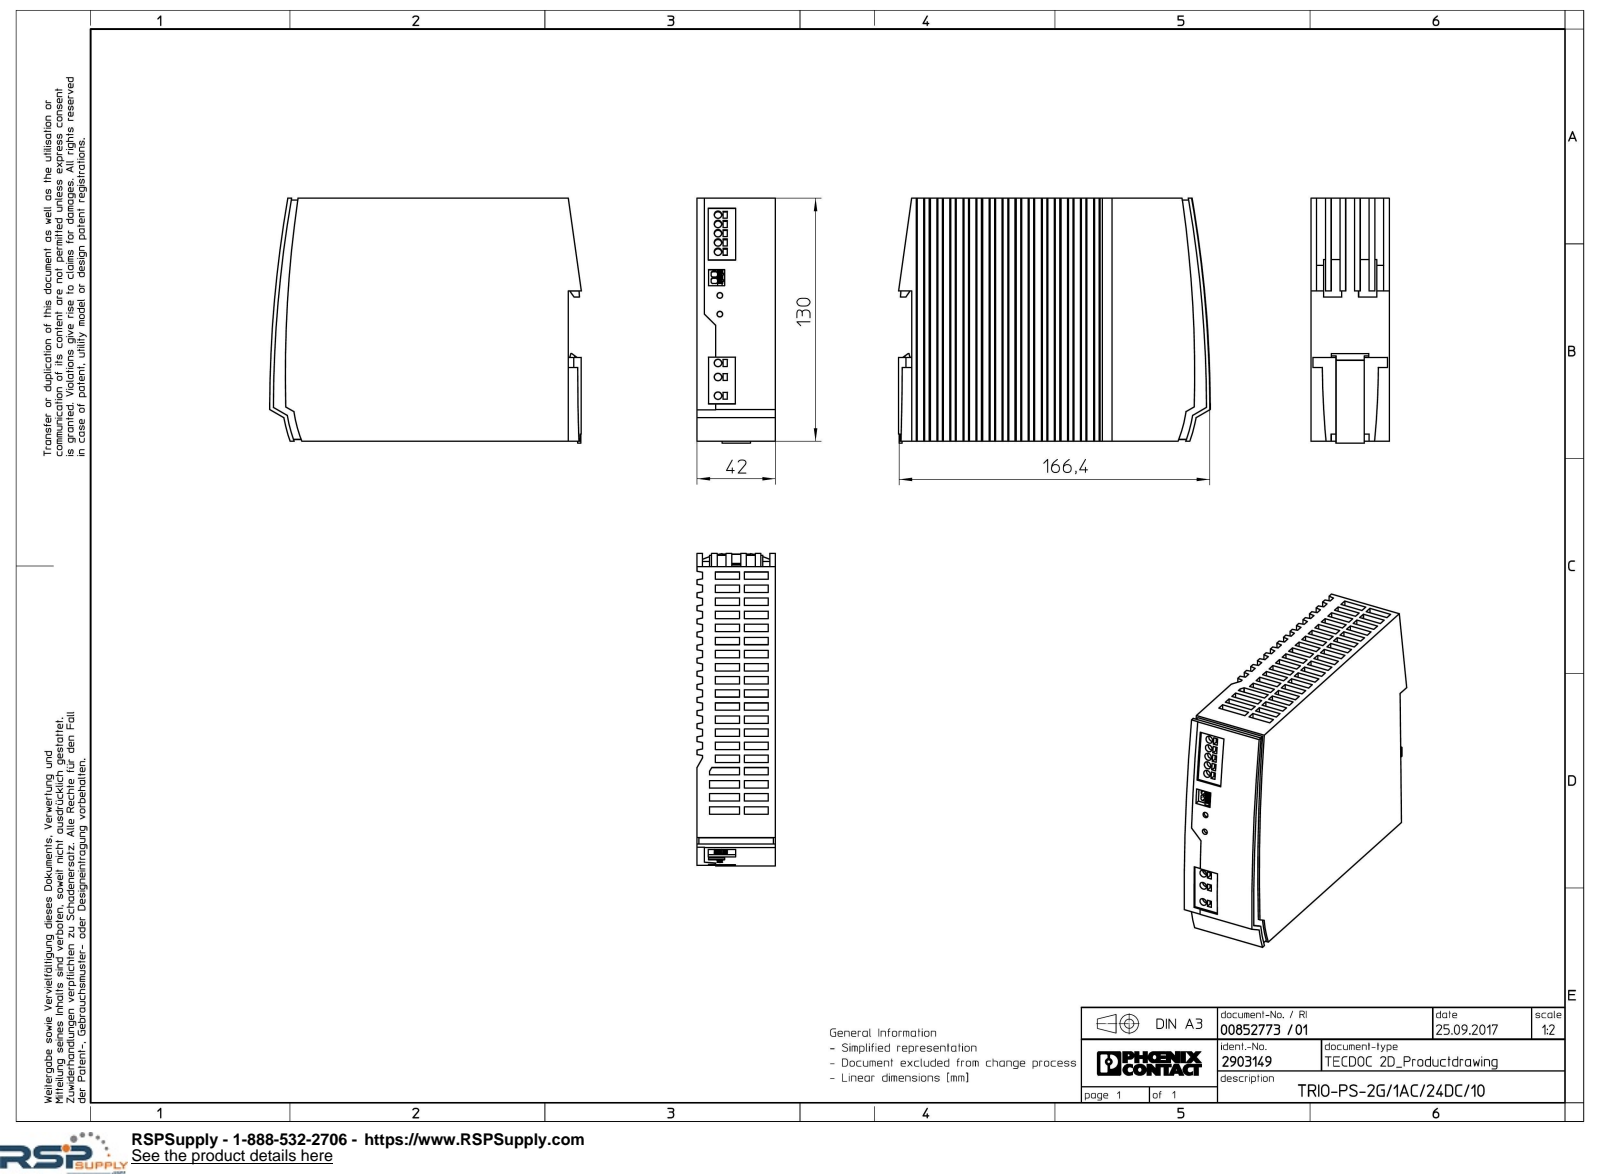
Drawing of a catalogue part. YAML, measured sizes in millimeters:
part_name: "TRIO_PS_2G_1AC_24DC_10-select"
step_written_by: "Creo Elements/Direct Modeling 20.1A 29-Sep-2018 (C) Parametric Technology GmbH (AUTOMOTIVE_DESIGN)"
units: millimeters
bodies: {solids: 1, faces: 694, planar: 647, cylindrical: 43, other: 4}
overall_size: [167, 131, 42]
volume: 826516
surface_area: 86353
round_holes:
  - {diameter: 4, count: 8}
  - {diameter: 3, count: 2}
partial_cylinders:
  - {radius: 0.57, count: 2}
  - {radius: 0.6, count: 2}
  - {radius: 1.03, count: 2}
  - {radius: 1.04, count: 2}
  - {radius: 430, count: 2}
  - {radius: 40, count: 1}
  - {radius: 46.1, count: 1}
  - {radius: 69.15, count: 1}
face_to_face_distances: [3, 42, 13.79, 27.58, 39, 41.37, 6.89, 6.9, 55.16, 20.68]
hole_center_spacings: [5, 10, 7.5, 10.03, 14.99, 15, 17.5, 19.99]
